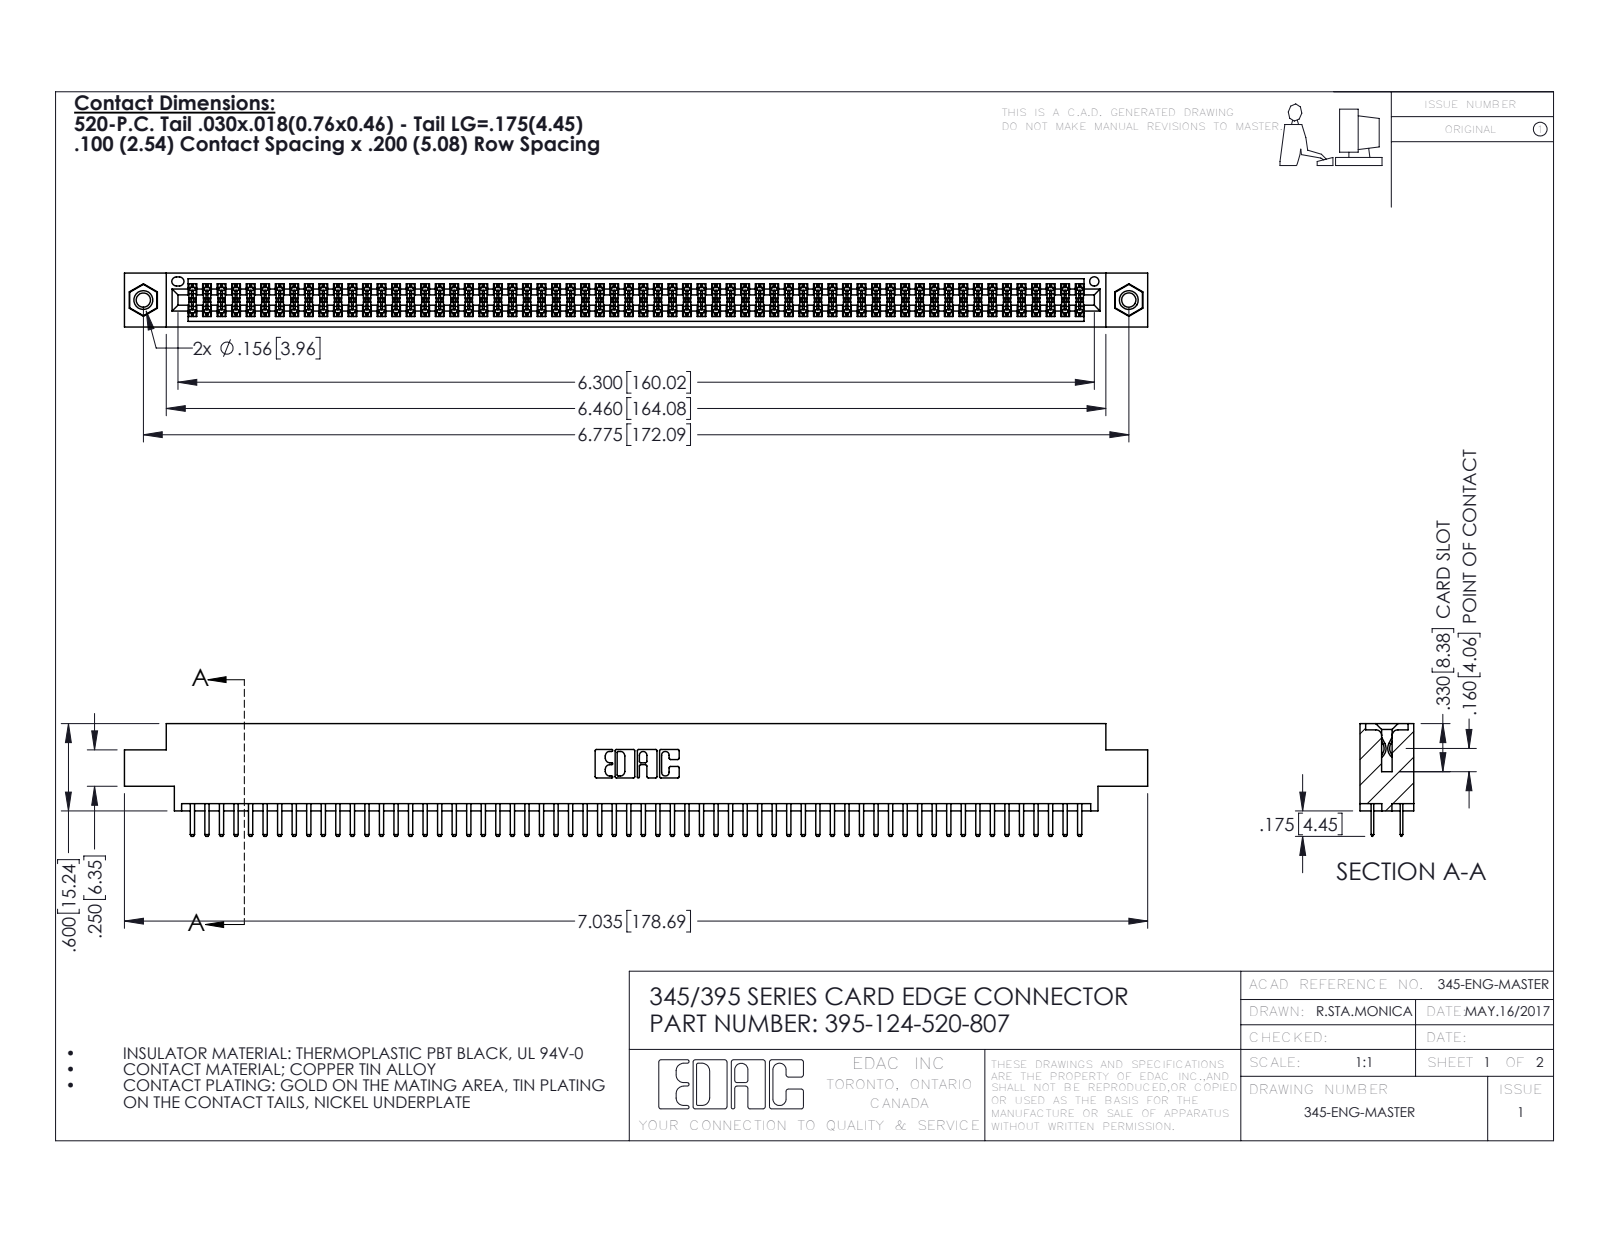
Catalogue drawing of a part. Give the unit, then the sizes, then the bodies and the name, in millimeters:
Units: millimetres
Overall size (bounding box): 178.7 × 19.7 × 9.4
Round holes (diameter × count): ⌀2.5 ×2, ⌀3.2 ×2, ⌀4 ×2, ⌀1.6 ×1
Round bosses / shafts (diameter × count): ⌀3.9 ×2
Partial cylindrical surfaces — rounded edges, fillets, slot ends (radius × count): R0.2 ×186, R0.3 ×128, R0.3 ×22, R0.2 ×6, R0.8 ×6, R0.7 ×3, R0.4 ×2, R0.5 ×2
Main face-to-face distances: 1.8, 7.6, 5.1, 9.4, 2.5, 6.9, 0.6, 5.7, 0.6, 1.8
Hole centre spacings: 6.9, 166.1, 172.1
Volume: 17 370 mm³ · Surface area: 26 110 mm²
Bodies: 127 solids, 6886 faces (4456 planar, 2414 cylindrical, 16 other)
Part name (STEP PRODUCT): 395-124-520-807; 345 Part_0.170 Offset - 0.156 Dia-TI; 345-292-001_345-293-120; 345-250-001_345-250-005-103
STEP written by: SolidWorks 2016 (CONFIG_CONTROL_DESIGN)
